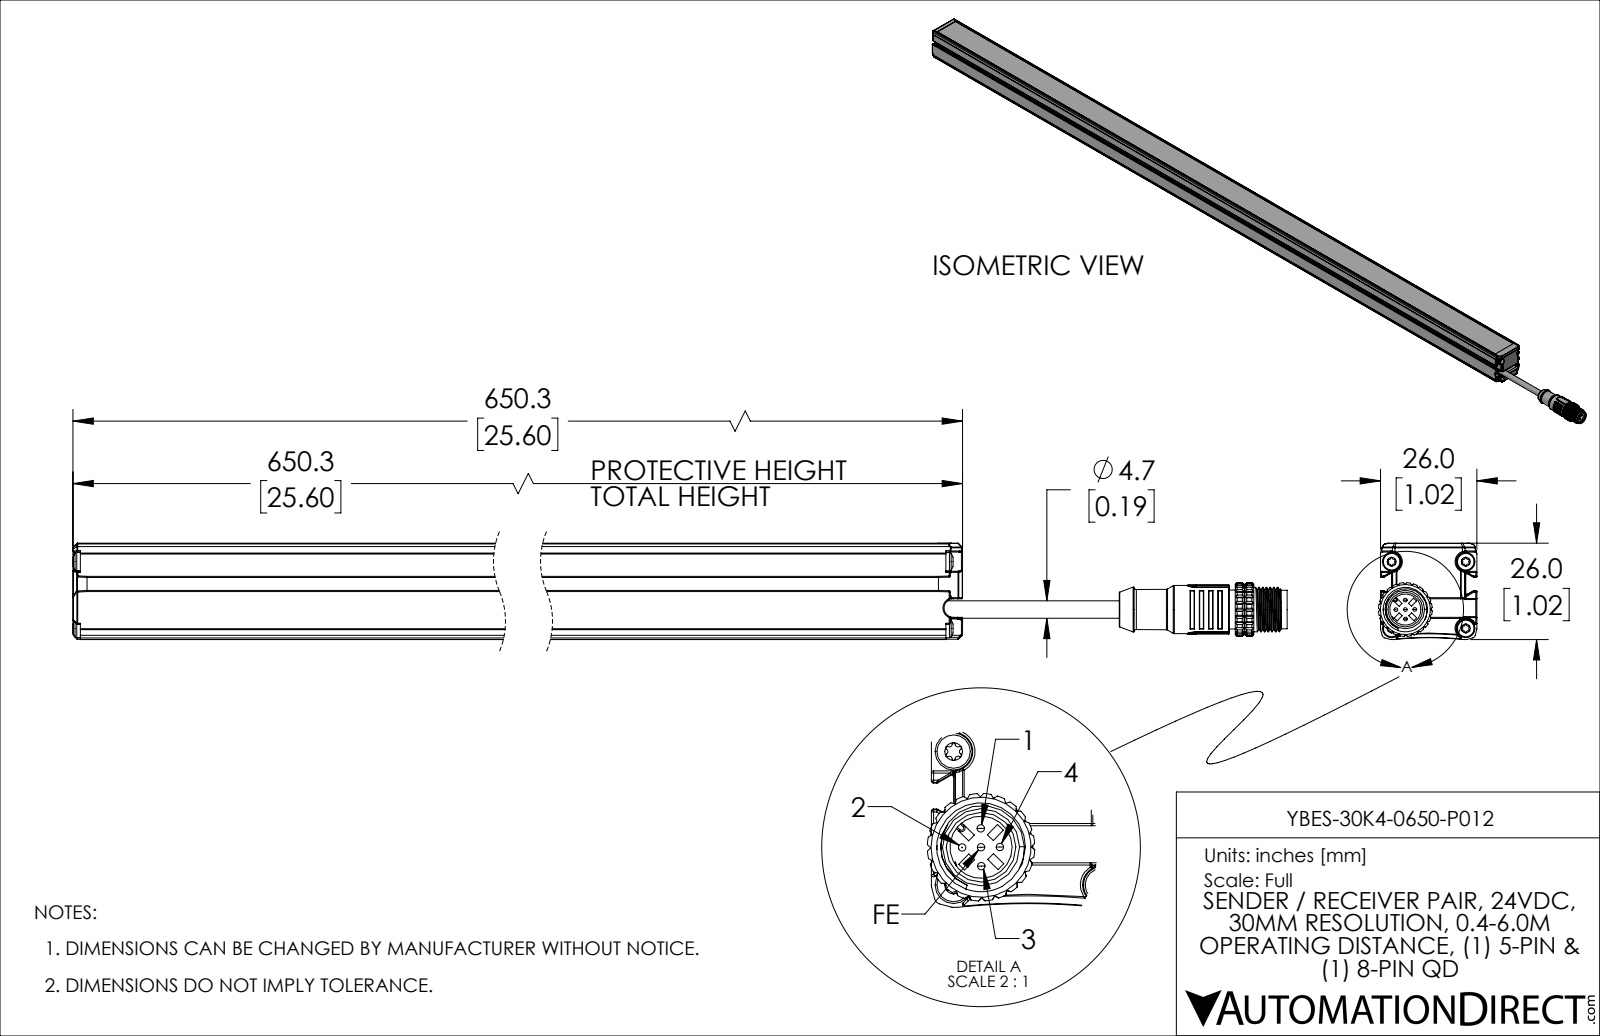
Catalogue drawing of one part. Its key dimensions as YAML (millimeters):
part_name: "YBES-30K4-0650-P012_REV1"
step_written_by: "SolidWorks 2019 (AUTOMOTIVE_DESIGN)"
units: millimeters
bodies: {solids: 2, faces: 1738, planar: 545, cylindrical: 719, other: 474}
overall_size: [737.9, 26.5, 26]
volume: 154900
surface_area: 168400
round_holes:
  - {diameter: 2.4, count: 4}
  - {diameter: 2.5, count: 4}
  - {diameter: 3.7, count: 4}
  - {diameter: 5, count: 4}
  - {diameter: 4.8, count: 1}
  - {diameter: 5.9, count: 1}
  - {diameter: 8.4, count: 1}
round_bosses_or_shafts:
  - {diameter: 1, count: 5}
  - {diameter: 3.2, count: 4}
  - {diameter: 2.5, count: 4}
  - {diameter: 1.3, count: 4}
  - {diameter: 1.5, count: 2}
  - {diameter: 13.5, count: 1}
  - {diameter: 13, count: 1}
  - {diameter: 12, count: 1}
partial_cylinders:
  - {radius: 0.2, count: 153}
  - {radius: 0.3, count: 115}
  - {radius: 0.2, count: 24}
  - {radius: 0.4, count: 24}
  - {radius: 1, count: 18}
  - {radius: 0.4, count: 16}
  - {radius: 0.2, count: 10}
  - {radius: 0.5, count: 7}
face_to_face_distances: [3, 1.5, 1.8, 21.2, 26, 18.2, 1.2, 0.4, 23, 4.8]
hole_center_spacings: [18, 20, 26.9, 6.3, 13.4, 17.1, 20.8]
